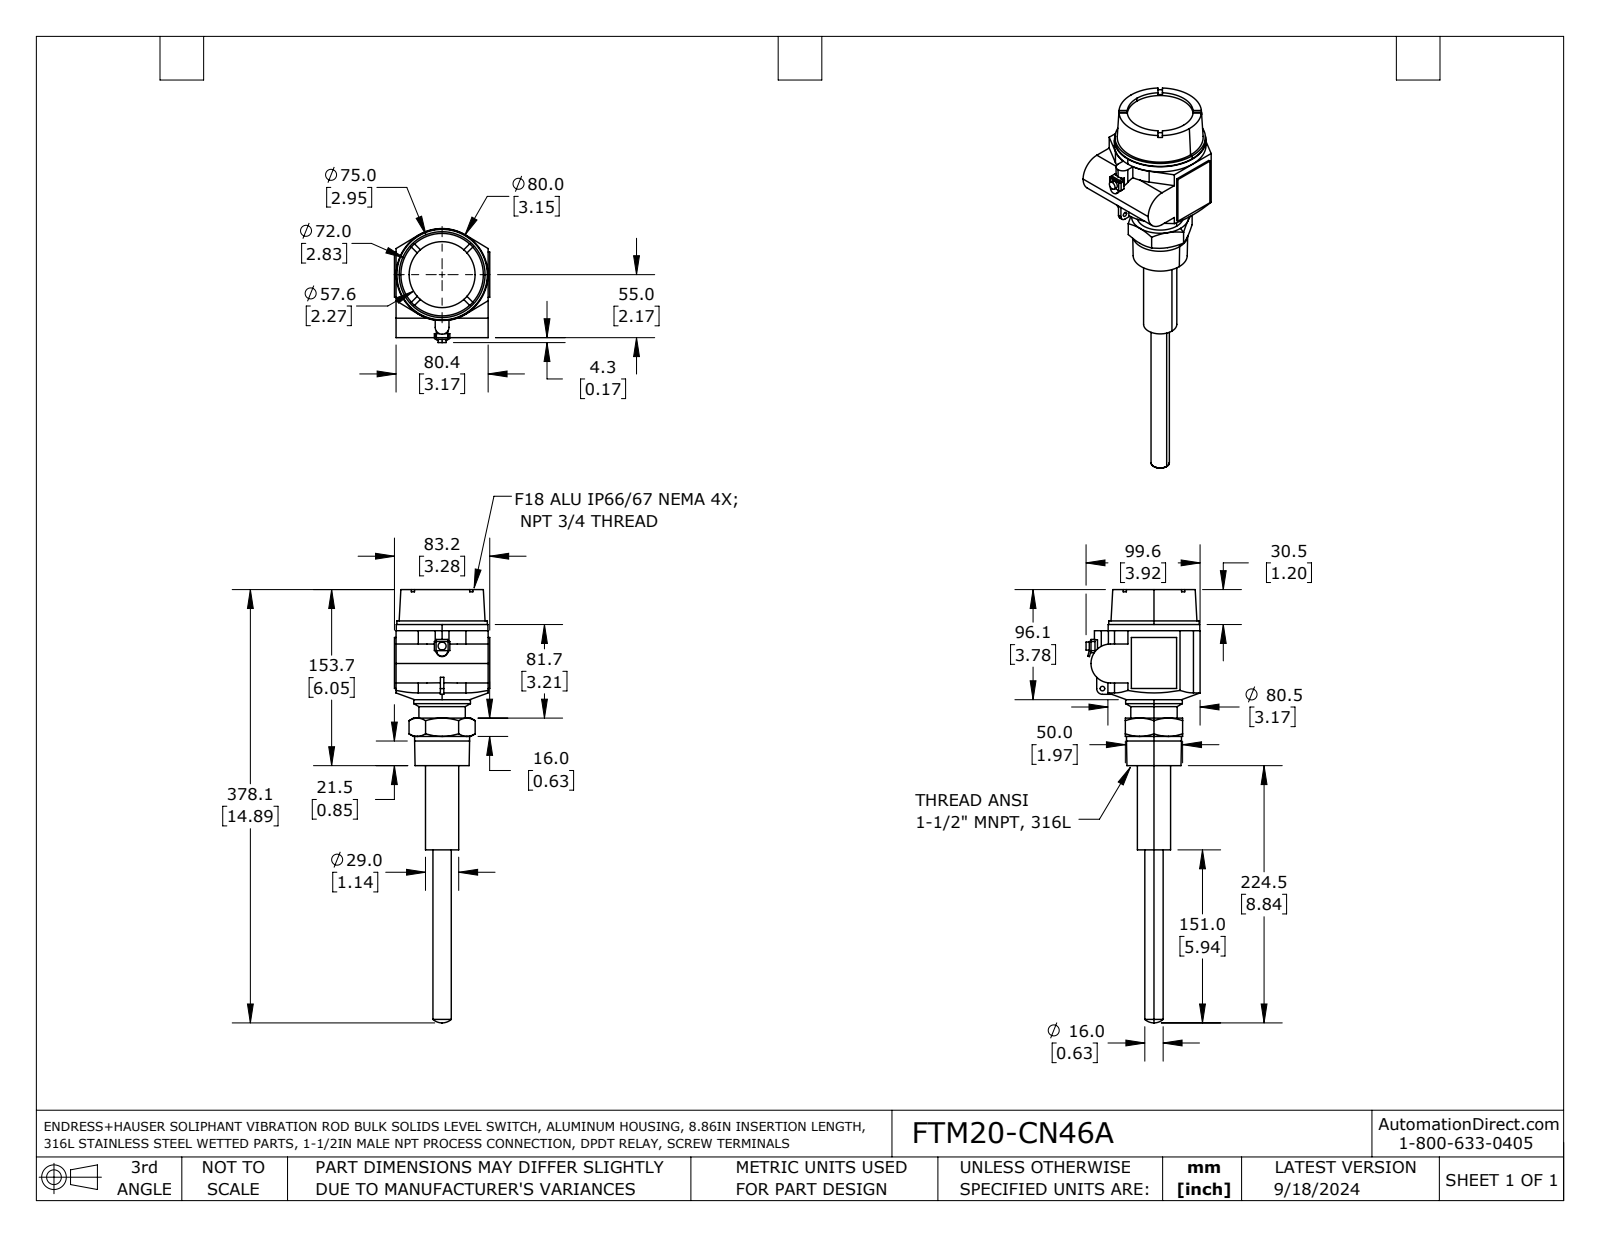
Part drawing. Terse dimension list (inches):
name: FTM20-CN46A
written by: SolidWorks 2021 (AUTOMOTIVE_DESIGN)
unit: in
bodies: 1 solid, 151 faces (88 planar, 36 cylindrical, 27 other)
size: 14.888 × 3.919 × 3.276
volume: 42.85 in³; area: 99.39 in²
holes: 1× ⌀0.157, 1× ⌀2.268
bosses: 1× ⌀3.15, 1× ⌀3.11, 1× ⌀1.949, 1× ⌀1.89, 1× ⌀1.594, 1× ⌀1.142, 1× ⌀0.63, 1× ⌀0.276
rounds: 3× R0.059, 2× R0.197, 1× R0.236, 1× R0.669, 1× R1.585
face distances: 0.055, 3.22, 3.276, 3.165, 0.118, 1.969, 5.931, 6.049, 3.169, 1.634
